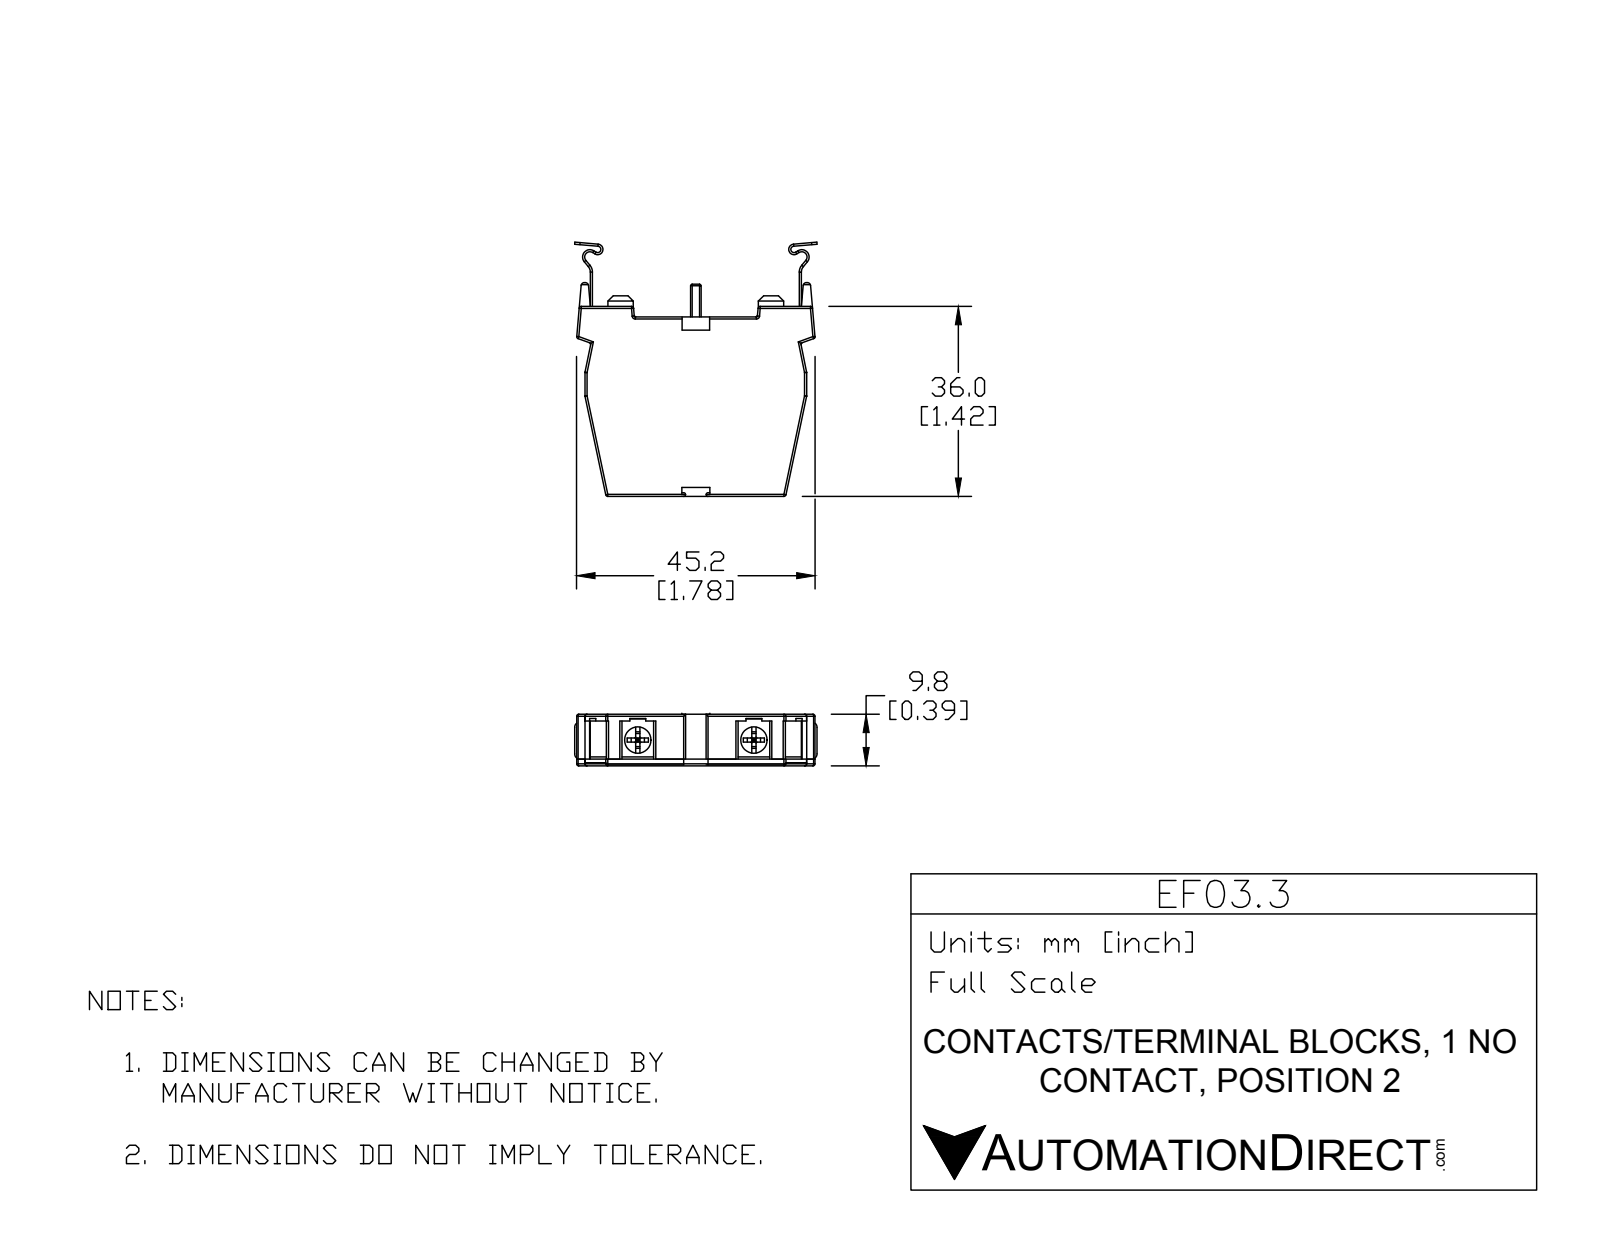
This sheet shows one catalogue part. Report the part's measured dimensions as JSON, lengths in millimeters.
{"part_name": "EF03.3", "step_written_by": "SolidWorks 2016 (AUTOMOTIVE_DESIGN)", "units": "millimeters", "bodies": {"solids": 7, "faces": 277, "planar": 155, "cylindrical": 100, "other": 22}, "overall_size": [48.16, 46.28, 9.8], "volume_mm3": 12160, "surface_area_mm2": 6664, "round_holes": [[5, 4]], "round_bosses_or_shafts": [[4.75, 2], [4, 2]], "partial_cylinders_radius": [[0.25, 44], [0.5, 8], [1, 6], [0.6, 4], [0.6, 2], [1, 2], [1.4, 2], [1.6, 2]], "face_to_face_distances": [9.8, 1.4, 8.4, 34, 7, 0.4, 2, 3.18, 37.18, 3.5], "hole_center_spacings": [21.81]}
